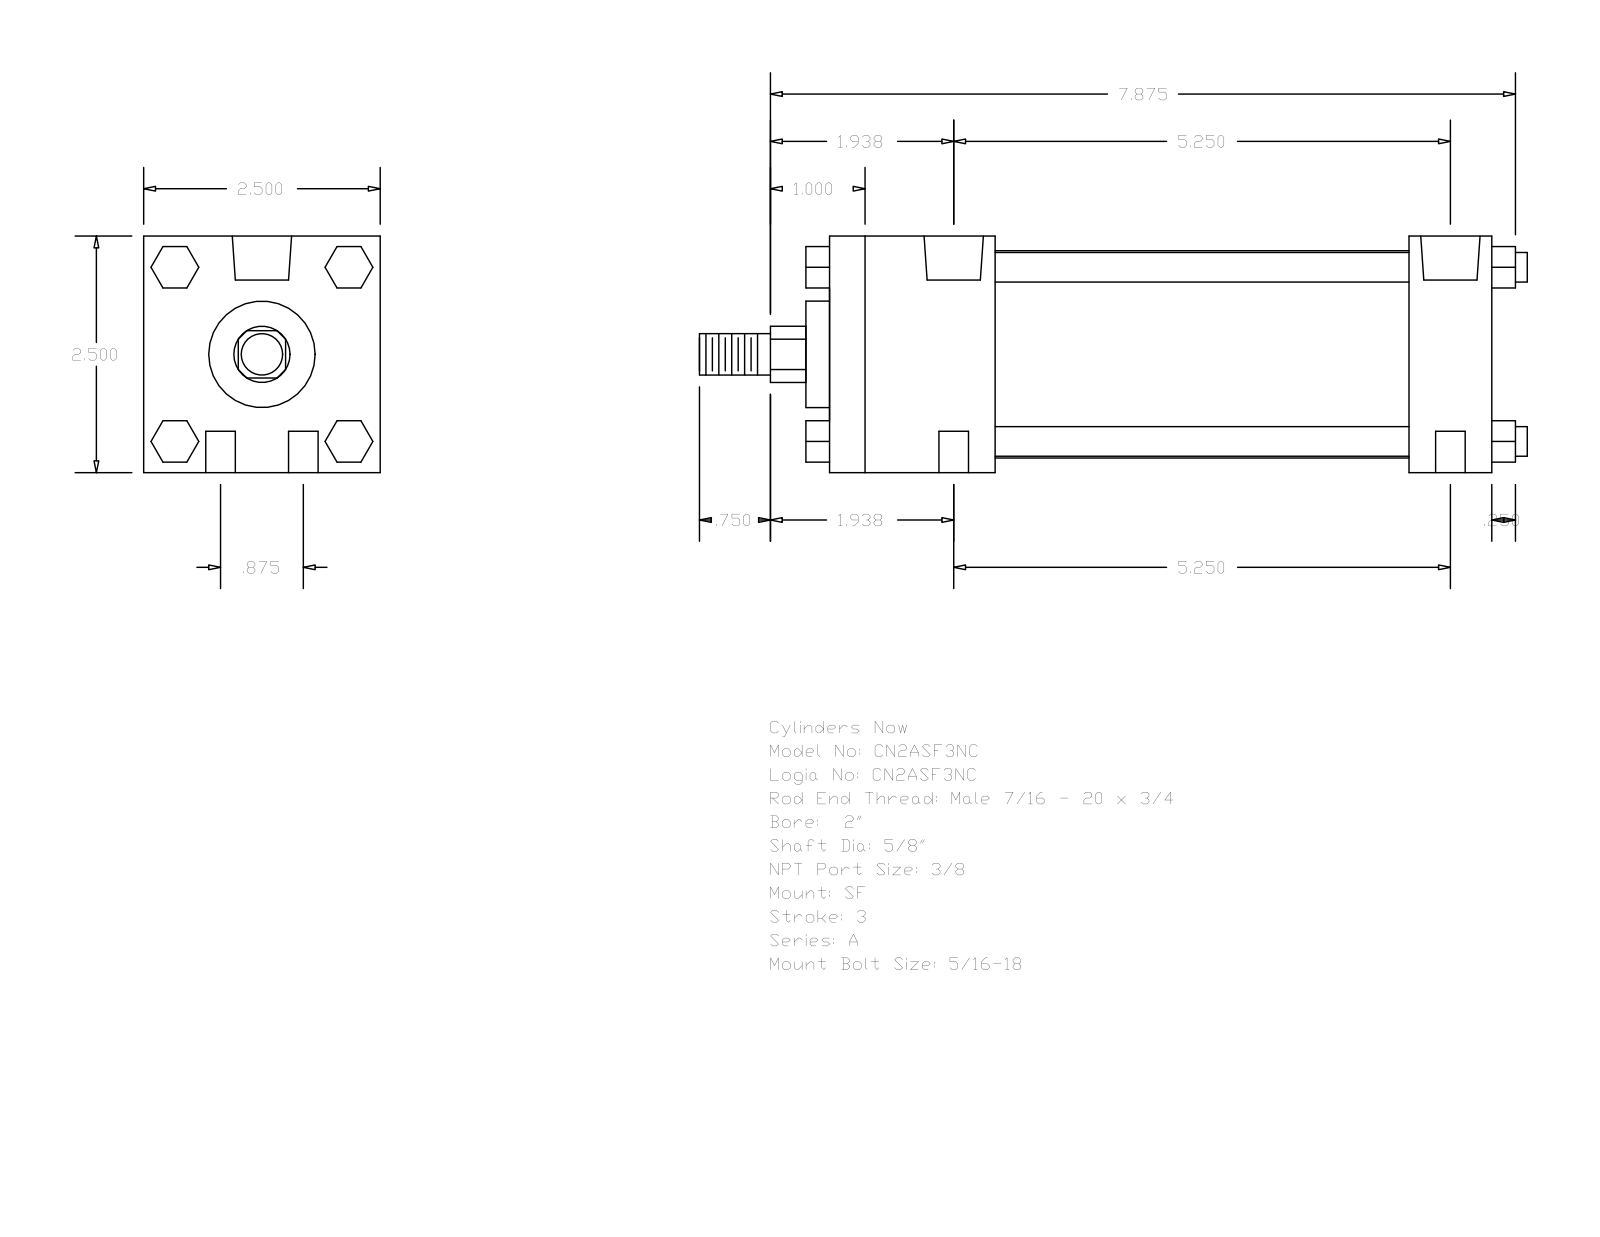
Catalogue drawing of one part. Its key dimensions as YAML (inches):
part_name: "A_SF__0200_0.625"
step_written_by: "GSSL Pune (CONFIG_CONTROL_DESIGN)"
units: inches
bodies: {solids: 0, faces: 124, planar: 94, cylindrical: 30, other: 0}
overall_size: [8.75, 2.5, 2.5]
round_holes:
  - {diameter: 0.313, count: 4}
  - {diameter: 0.219, count: 2}
  - {diameter: 0.627, count: 2}
round_bosses_or_shafts:
  - {diameter: 0.313, count: 4}
  - {diameter: 2.19, count: 1}
  - {diameter: 1.125, count: 1}
  - {diameter: 0.625, count: 1}
  - {diameter: 0.437, count: 1}
partial_cylinders:
  - {radius: 0.297, count: 1}
face_to_face_distances: [2.5, 7, 6.125, 0.875, 1.75, 4.375, 5.25, 0.25, 7.25, 2]
hole_center_spacings: [0.437, 5.268, 5.25, 0.875, 5.322, 4.937]
